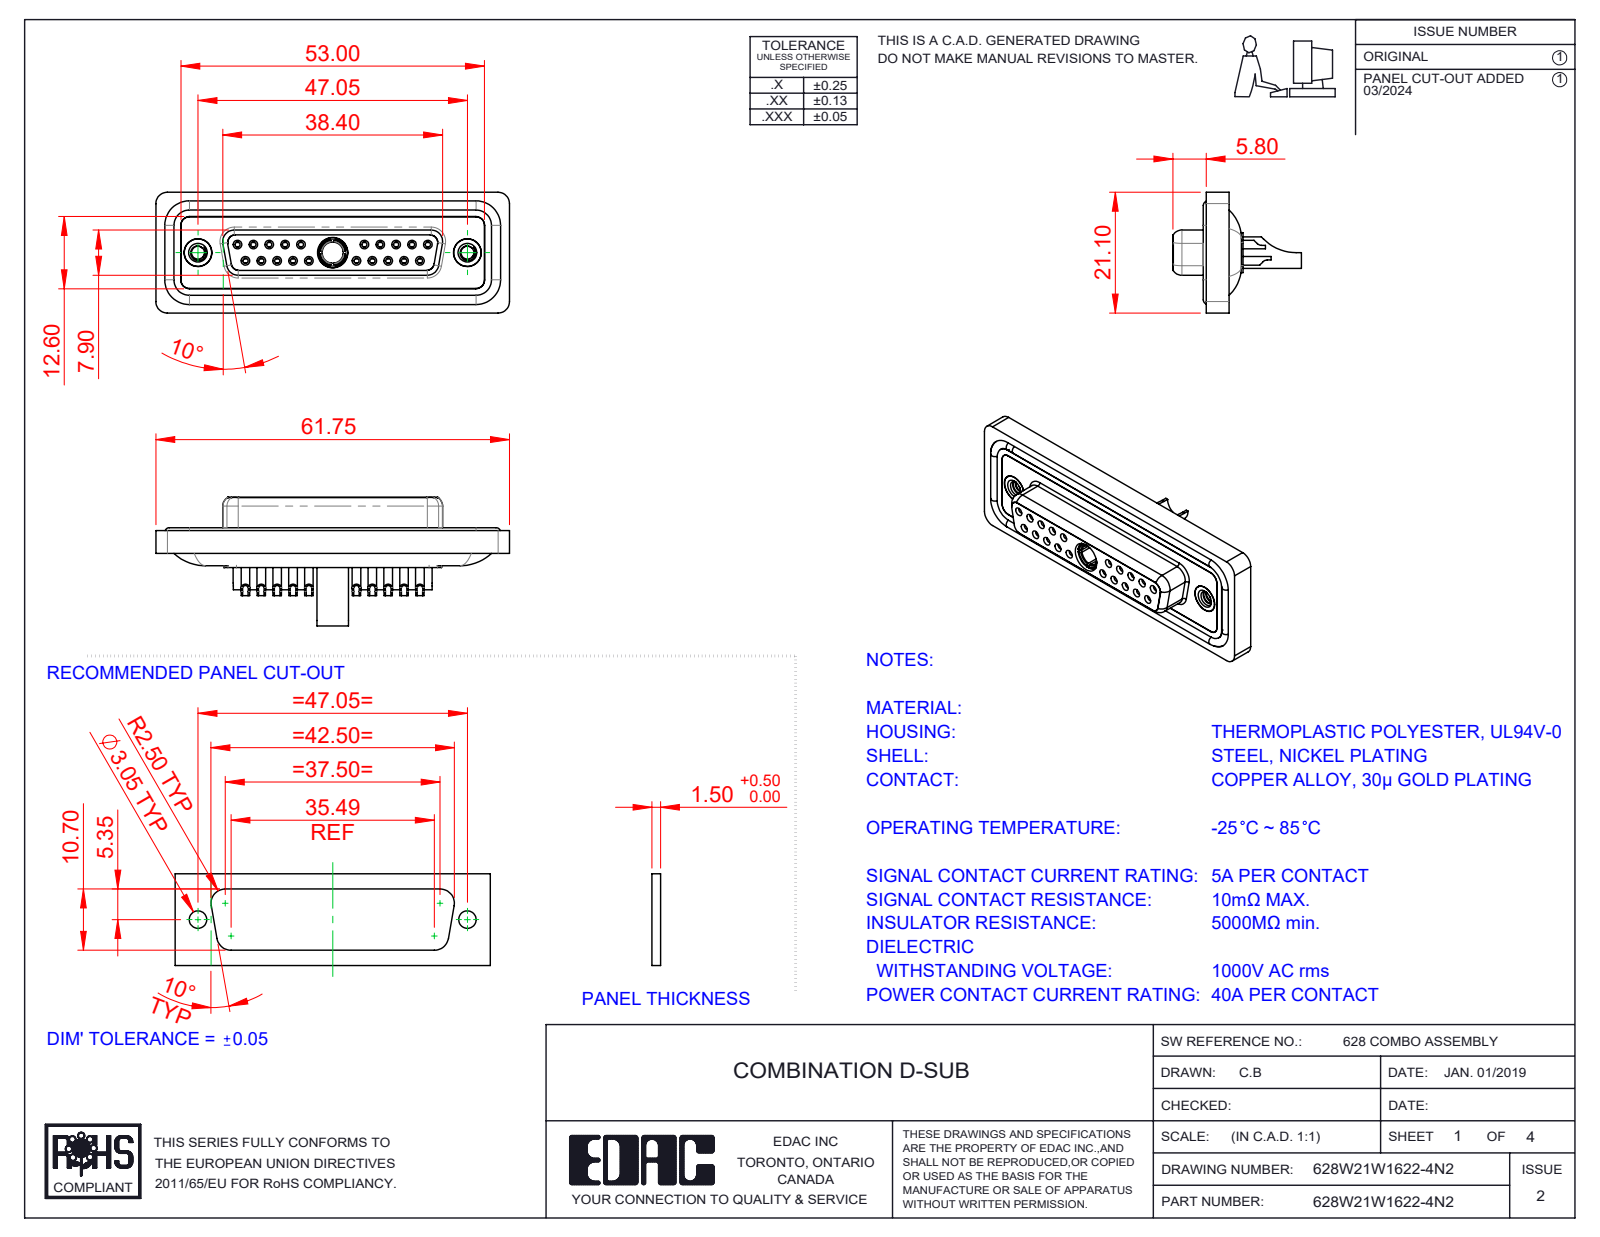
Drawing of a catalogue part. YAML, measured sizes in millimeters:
part_name: "628W21W1622-4N2; 628Combo Contact Row 2_22; 628Combo Contact Row 1_22; 628Combo Shell Rear_25 Contacts (+5 more)"
step_written_by: "SolidWorks 2023 (CONFIG_CONTROL_DESIGN)"
units: millimeters
bodies: {solids: 29, faces: 1563, planar: 476, cylindrical: 632, other: 455}
overall_size: [61.75, 22.45, 21.1]
volume: 8455
surface_area: 14352
round_holes:
  - {diameter: 0.9, count: 20}
  - {diameter: 1, count: 20}
  - {diameter: 1.1, count: 20}
  - {diameter: 1.5, count: 20}
  - {diameter: 2, count: 20}
  - {diameter: 1.6, count: 10}
  - {diameter: 1.7, count: 10}
  - {diameter: 4.85, count: 3}
  - {diameter: 2.26, count: 2}
  - {diameter: 4, count: 2}
  - {diameter: 4.05, count: 2}
  - {diameter: 5, count: 2}
round_bosses_or_shafts:
  - {diameter: 2.2, count: 20}
  - {diameter: 1.6, count: 14}
  - {diameter: 4.95, count: 2}
  - {diameter: 4.8, count: 2}
  - {diameter: 5.5, count: 1}
  - {diameter: 5.2, count: 1}
  - {diameter: 4.96, count: 1}
  - {diameter: 4.75, count: 1}
partial_cylinders:
  - {radius: 1.5, count: 22}
  - {radius: 2, count: 18}
  - {radius: 1.35, count: 8}
  - {radius: 1.6, count: 8}
  - {radius: 1, count: 6}
  - {radius: 0.25, count: 4}
  - {radius: 0.5, count: 4}
  - {radius: 0.6, count: 4}
face_to_face_distances: [0.4, 1.8, 7.45, 5.65, 6.6, 0.5, 1.6, 7.05, 2.9, 1.1]
hole_center_spacings: [3.16, 2.77, 5.54, 5.03, 8.31, 7.48, 16.62, 19.39]
